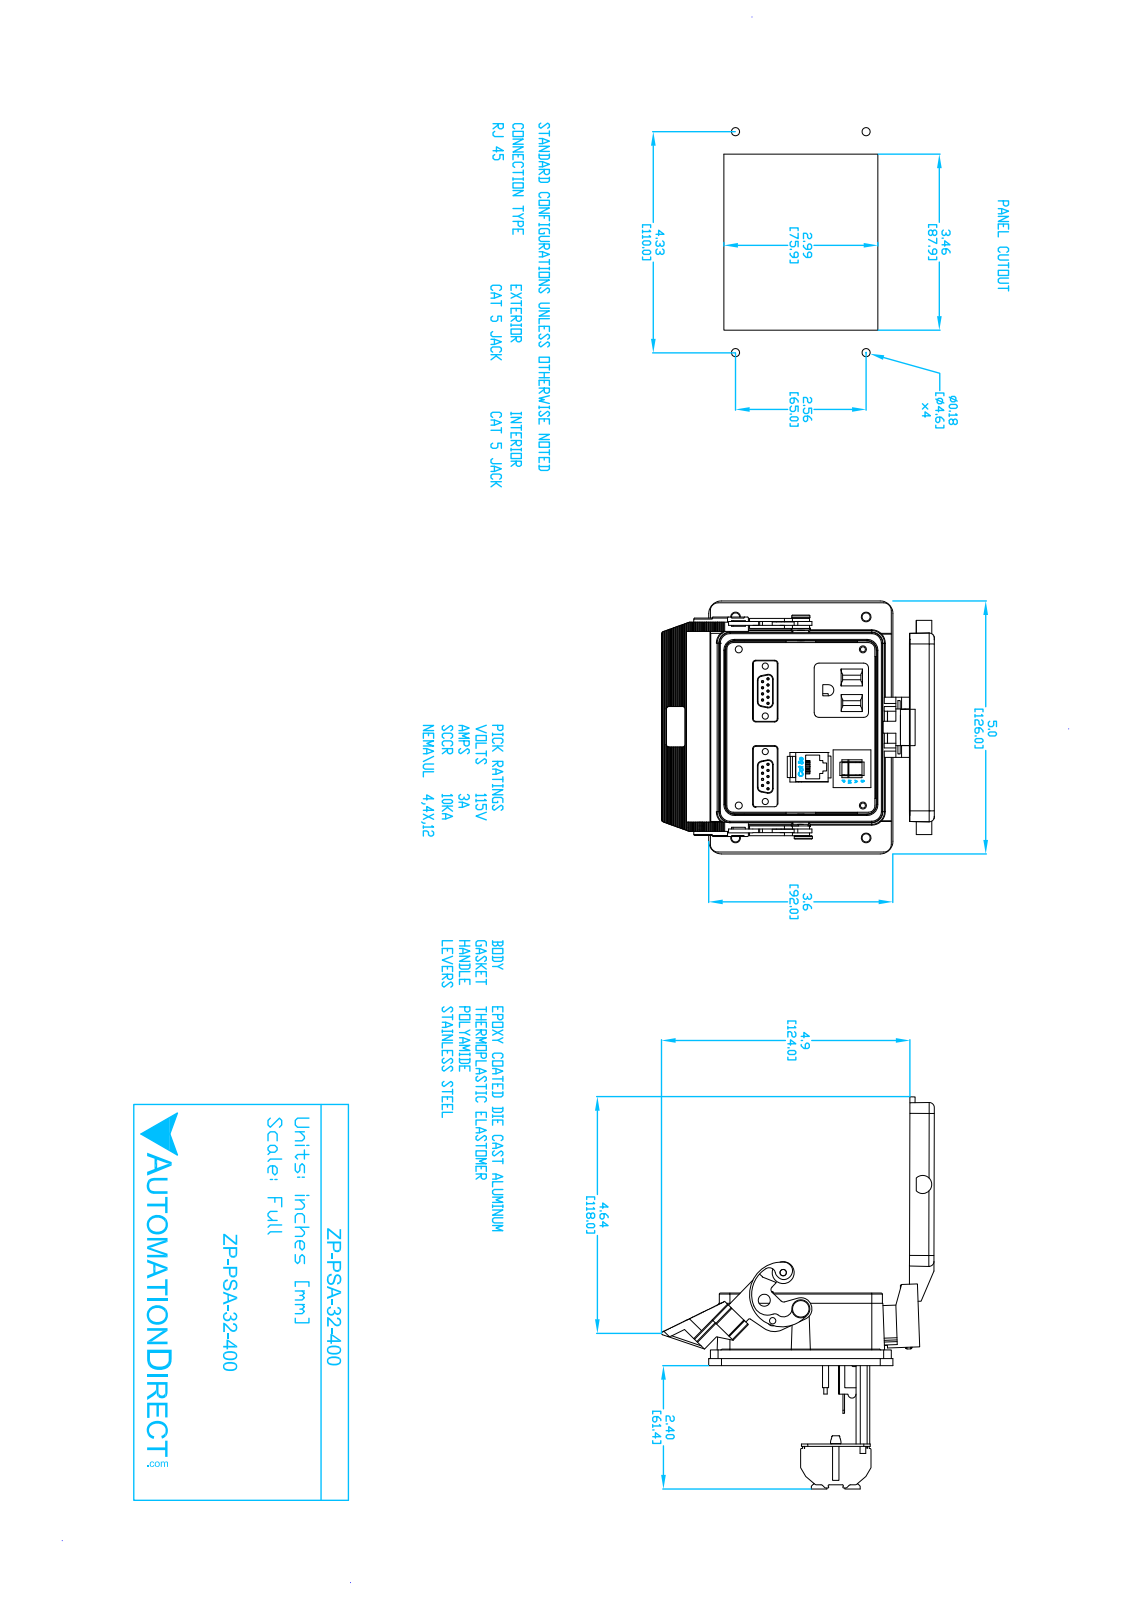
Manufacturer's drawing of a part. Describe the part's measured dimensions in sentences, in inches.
The part is named "ZP-PSA-32-400". Its 3-D file was written by "SolidWorks 2017 (AUTOMOTIVE_DESIGN)". It is 1 solid with 3646 faces: 2201 planar, 764 cylindrical and 681 other. Overall it measures 7.723 by 5.313 by 4.96 inches. Its volume is 12.11 cubic inches and its surface area 189.1 square inches. Round holes: 18 of diameter 0.045, 8 of diameter 0.144, 6 of diameter 0.098, 6 of diameter 0.173, 4 of diameter 0.09, 4 of diameter 0.122, 4 of diameter 0.132, 4 of diameter 0.134, 4 of diameter 0.16, 4 of diameter 0.19, 3 of diameter 0.091, 2 of diameter 0.097. Round bosses or shafts: 18 of diameter 0.038, 4 of diameter 0.22, 4 of diameter 0.118, 4 of diameter 0.109, 3 of diameter 0.205, 2 of diameter 0.354, 2 of diameter 0.175, 2 of diameter 0.096. Partial cylindrical surfaces (rounded edges, fillets, slot ends): 22 of radius 0.02, 18 of radius 0.1, 12 of radius 0.005, 12 of radius 0.025, 12 of radius 0.25, 10 of radius 0.013, 9 of radius 0.015, 9 of radius 0.109. The main face-to-face distances are 0.135, 0.847, 0.06, 0.907, 1.596, 2.443, 2.503, 1.843, 0.247, 0.6. The hole center spacings are 0.12, 0.472, 3.867, 0.125, 0.236, 1.287, 1.569, 3.97.
